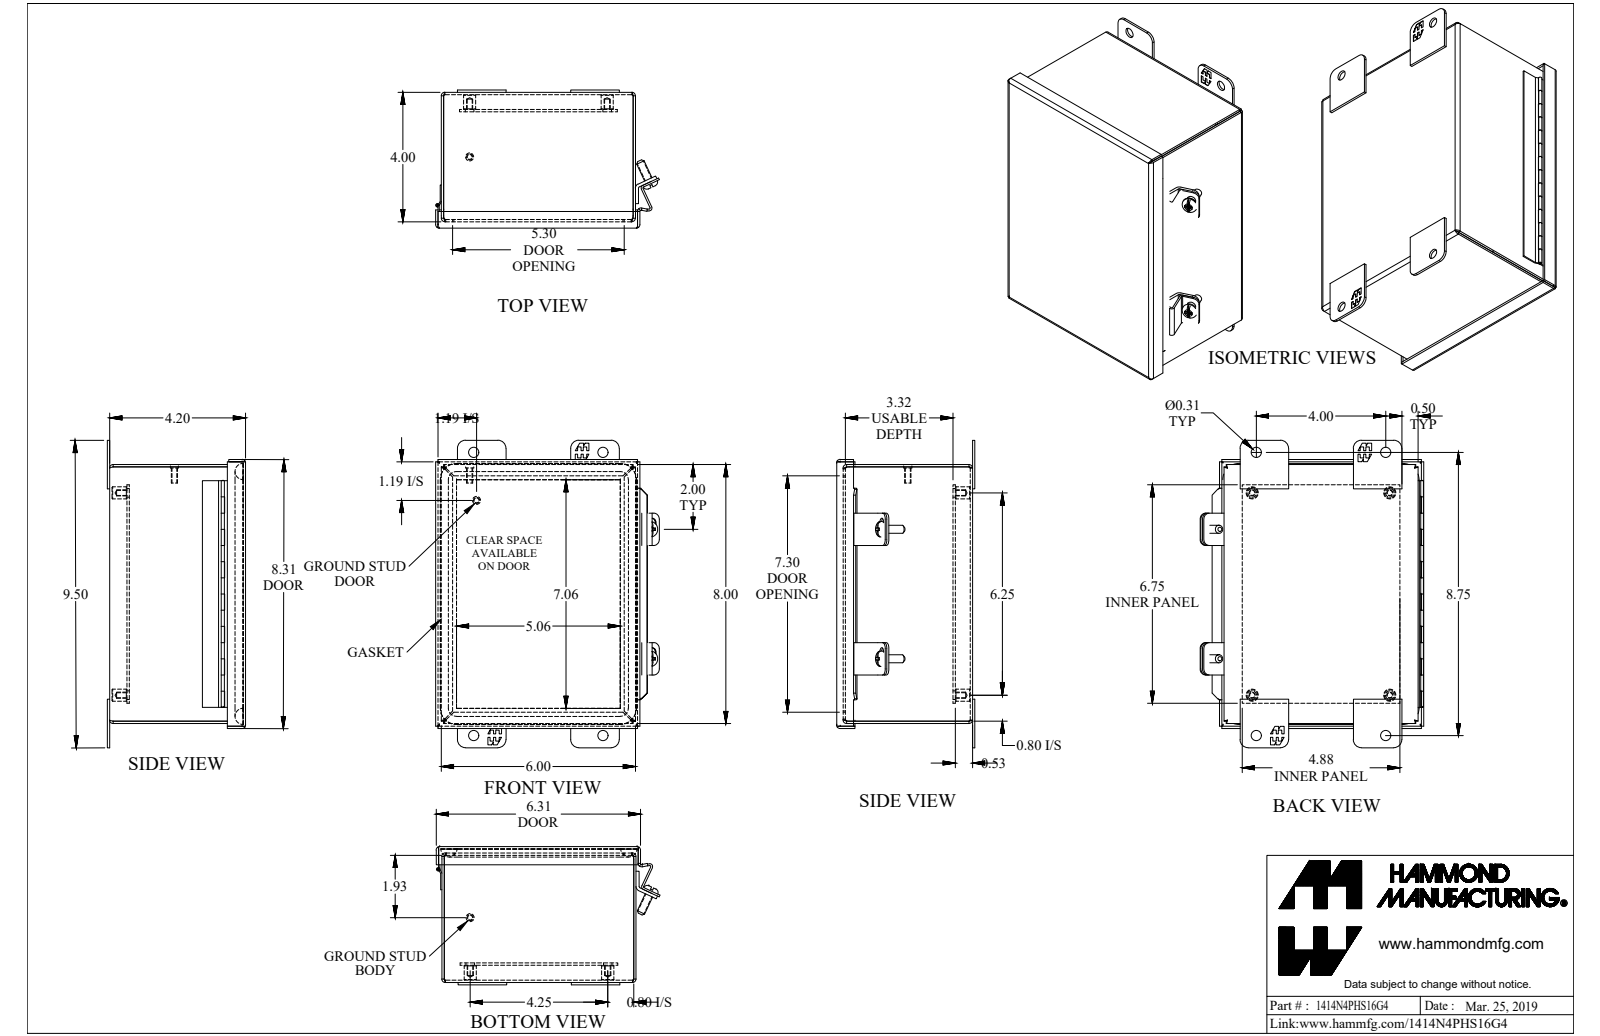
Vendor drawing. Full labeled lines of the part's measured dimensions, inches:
Part name (STEP PRODUCT): 1414N4PHS16G4
STEP written by: SolidWorks 2018 (AUTOMOTIVE_DESIGN)
Units: inches
Bodies: 21 solids, 649 faces (427 planar, 164 cylindrical, 58 other)
Overall size (bounding box): 9.5 × 6.903 × 4.269
Volume: 23.6 in³ · Surface area: 650.2 in²
Round holes (diameter × count): ⌀0.156 ×4, ⌀0.265 ×4, ⌀0.313 ×4, ⌀0.213 ×2, ⌀0.05 ×1
Round bosses / shafts (diameter × count): ⌀0.375 ×4, ⌀0.25 ×4, ⌀0.48 ×2, ⌀0.19 ×2, ⌀0.1 ×1, ⌀0.045 ×1
Partial cylindrical surfaces — rounded edges, fillets, slot ends (radius × count): R0.25 ×24, R0.036 ×8, R0.108 ×8, R0.188 ×8, R0.079 ×4, R0.118 ×4, R0.141 ×4, R0.499 ×4
Main face-to-face distances: 0.072, 0.532, 0.081, 5.928, 4.116, 4.197, 4.125, 4.044, 7.928, 0.604
Hole centre spacings: 1.256, 6.25, 7.501, 7.558, 8.559, 4, 4.31, 4.31
